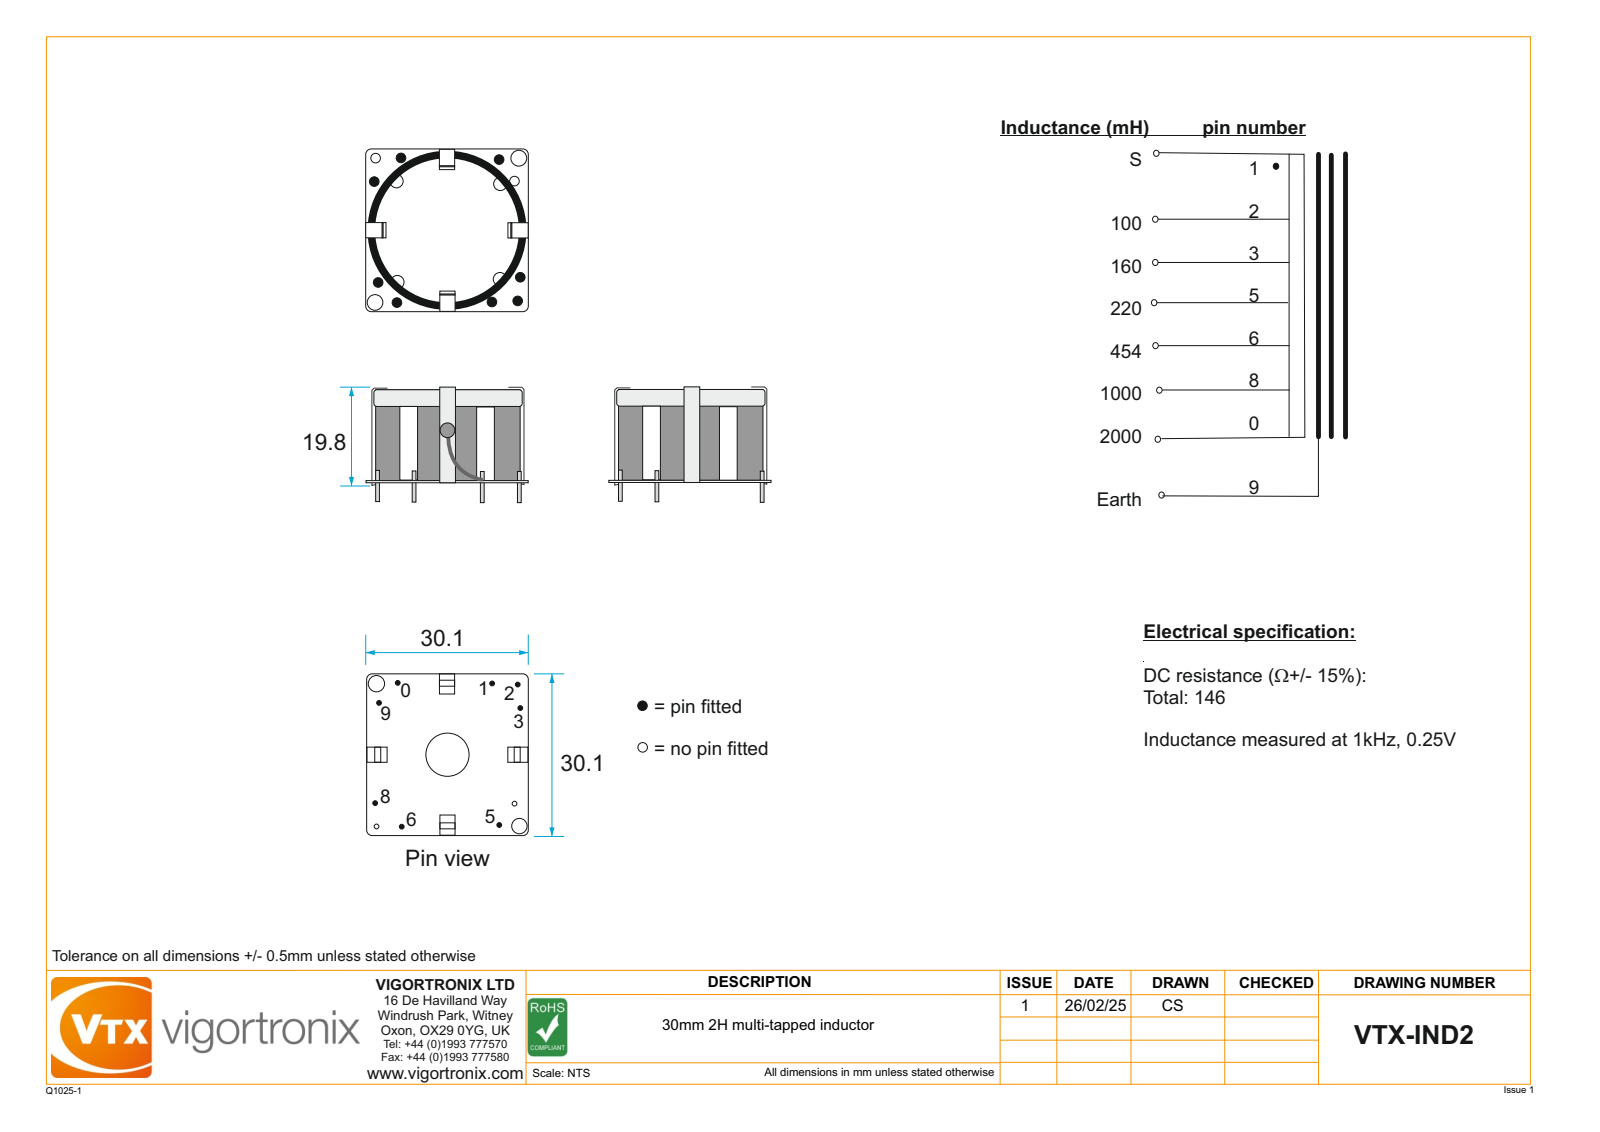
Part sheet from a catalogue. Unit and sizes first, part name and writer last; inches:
Units: inches
Overall size (bounding box): 1.192 × 1.192 × 0.933
Round holes (diameter × count): ⌀0.039 ×10, ⌀0.079 ×2, ⌀0.118 ×2, ⌀0.098 ×1, ⌀0.217 ×1, ⌀0.394 ×1, ⌀0.461 ×1, ⌀0.839 ×1, ⌀0.874 ×1, ⌀1.035 ×1
Round bosses / shafts (diameter × count): ⌀0.098 ×2, ⌀1.083 ×1, ⌀0.496 ×1, ⌀0.453 ×1
Partial cylindrical surfaces — rounded edges, fillets, slot ends (radius × count): R0.004 ×40, R0.01 ×10, R0.039 ×8, R0.055 ×8, R0.059 ×8, R0.02 ×4, R0.026 ×4, R0.033 ×4
Main face-to-face distances: 0.071, 0.703, 0.632, 0.53, 0.102, 0.016, 0.315, 0.317, 0.213, 0.215
Hole centre spacings: 0.2, 0.583, 0.8, 0.825, 1, 1.02, 1.281, 0.197
Volume: 0.415 in³ · Surface area: 19.31 in²
Bodies: 55 solids, 702 faces (206 planar, 269 cylindrical, 227 other)
Part name (STEP PRODUCT): Large Pot Core Ring; Wire Green; Wire brown; Large Pot Core Coil (+8 more)
STEP written by: SolidWorks 2024 (AUTOMOTIVE_DESIGN)
